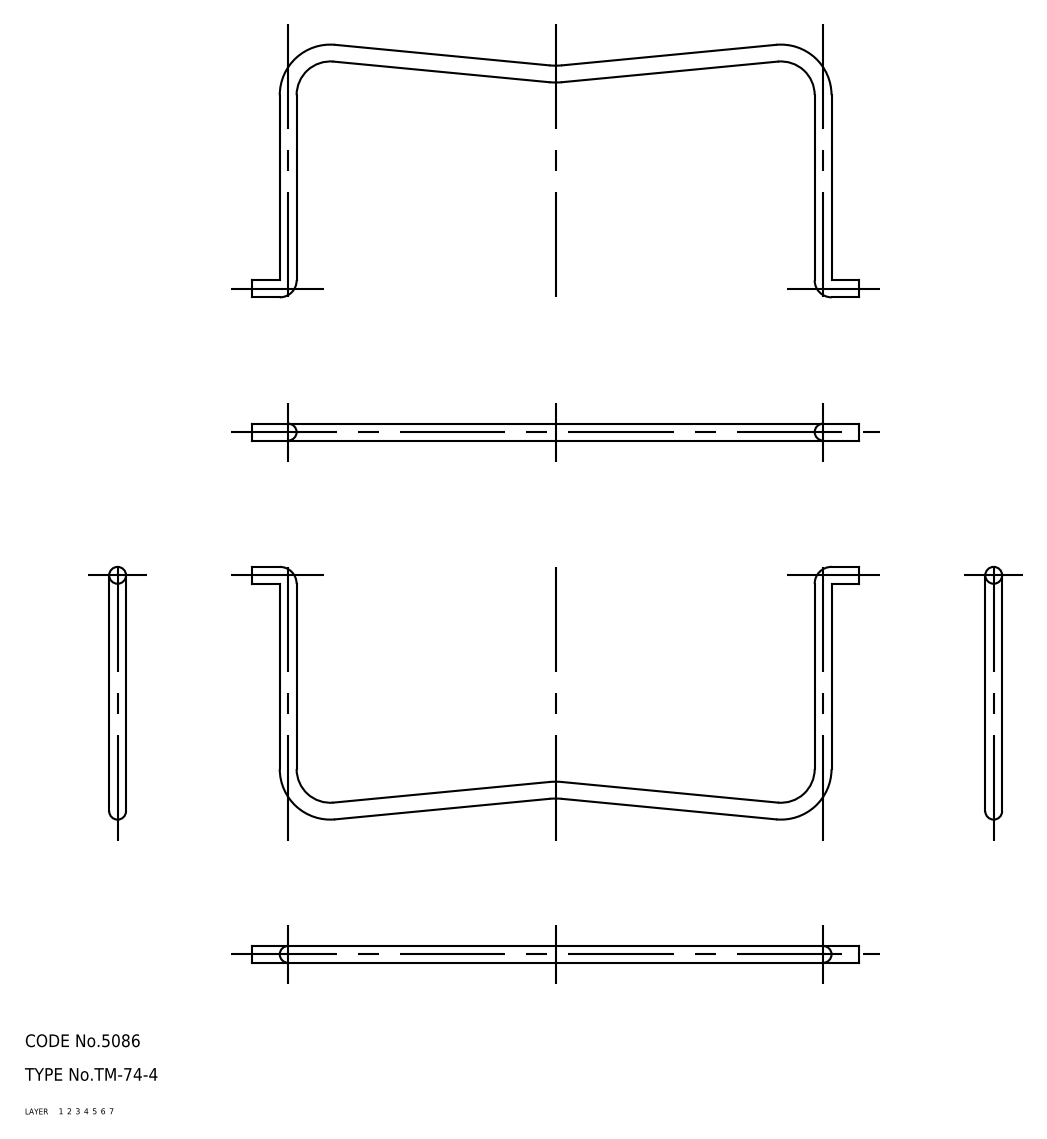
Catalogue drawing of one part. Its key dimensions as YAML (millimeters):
part_name: "67109589"
step_written_by: "CADfix (AUTOMOTIVE_DESIGN)"
units: millimeters
bodies: {solids: 1, faces: 4, planar: 0, cylindrical: 0, other: 4}
overall_size: [144, 60, 4]
volume: 3221
surface_area: 3106
